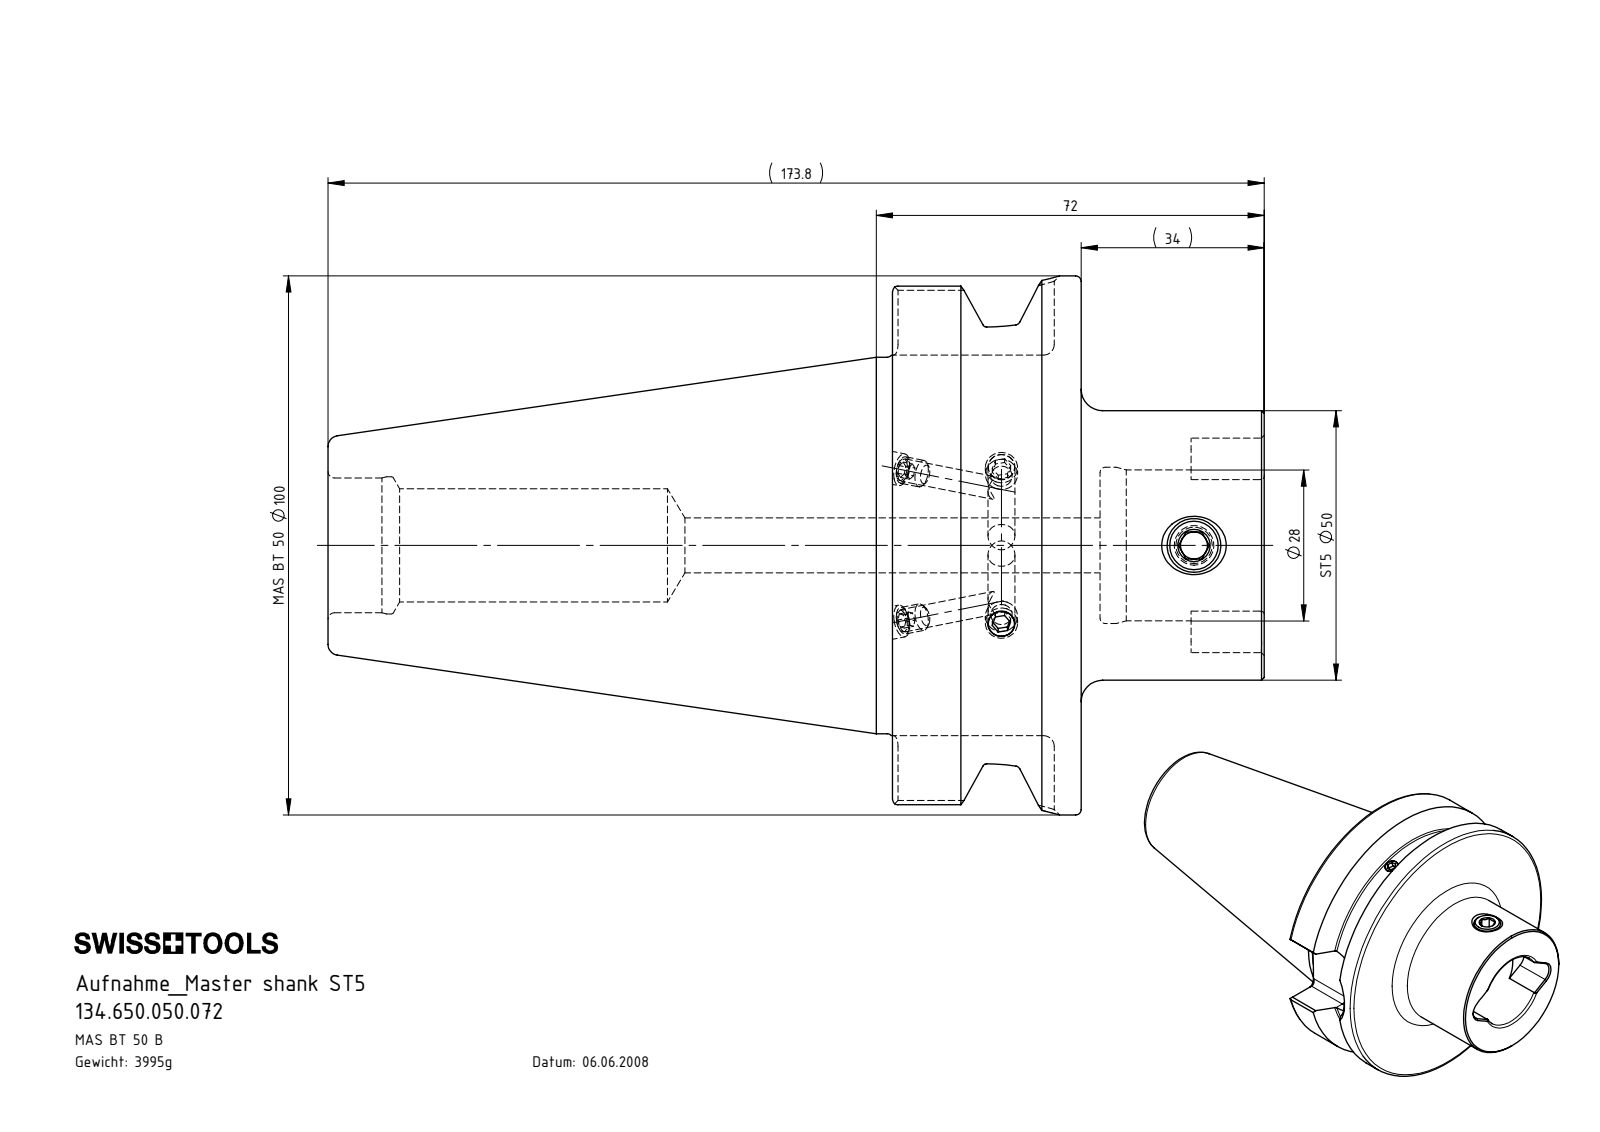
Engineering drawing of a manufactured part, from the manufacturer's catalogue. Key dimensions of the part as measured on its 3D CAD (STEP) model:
Part name (STEP PRODUCT): ISO 4026 - M6 x 5; ST5-ER1.001.012_A; BB5-ST5.K01.072; BB5-ST5.K01.072_A_mit Bundkhlung
STEP written by: SolidWorks 2015 (CONFIG_CONTROL_DESIGN)
Units: millimetres
Bodies: 3 solids, 168 faces (45 planar, 53 cylindrical, 70 other)
Overall size (bounding box): 173.8 × 100 × 100
Volume: 508 521 mm³ · Surface area: 61 561 mm²
Round holes (diameter × count): ⌀6 ×2, ⌀5 ×1, ⌀9 ×1, ⌀10.2 ×1, ⌀21 ×1, ⌀25 ×1, ⌀25.45 ×1, ⌀28 ×1, ⌀29 ×1
Round bosses / shafts (diameter × count): ⌀100 ×1, ⌀85 ×1, ⌀69.85 ×1, ⌀50 ×1, ⌀10 ×1, ⌀6 ×1
Partial cylindrical surfaces — rounded edges, fillets, slot ends (radius × count): R2 ×8, R4.2 ×2, R12.85 ×1
Main face-to-face distances: 35, 69, 34, 70.6, 38.5, 3.5, 30.5, 104.8, 139.8, 143.3
